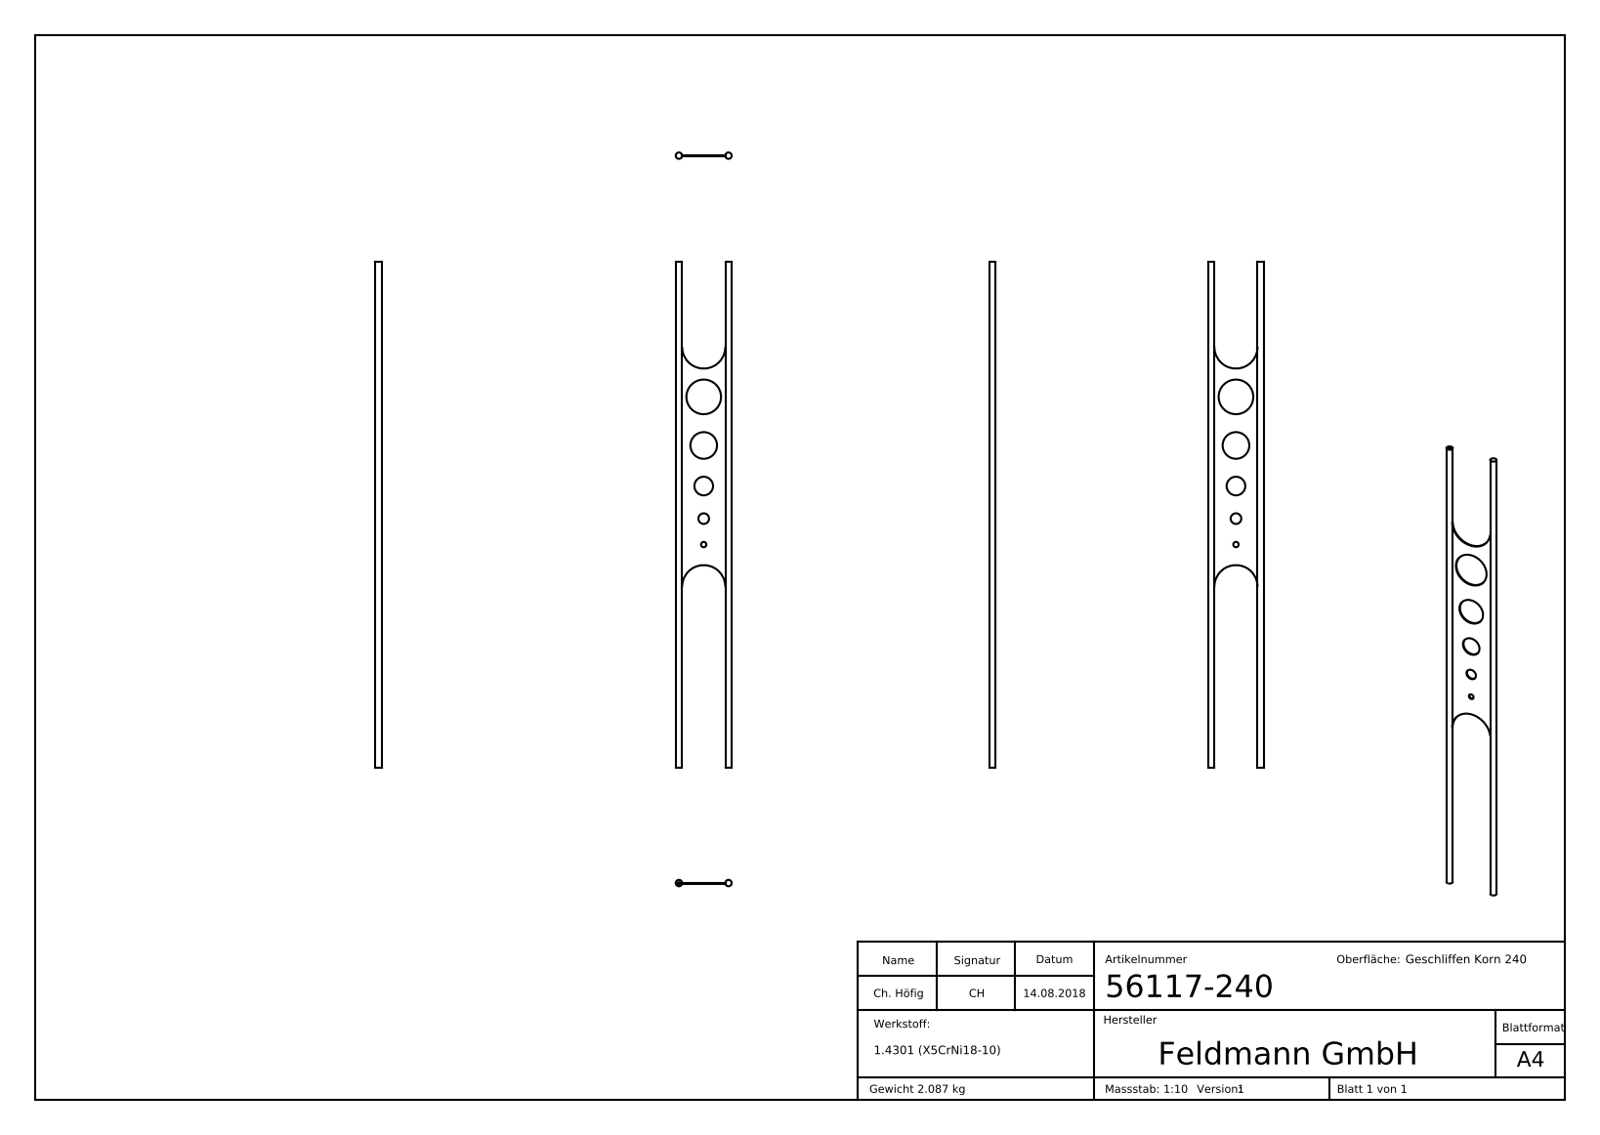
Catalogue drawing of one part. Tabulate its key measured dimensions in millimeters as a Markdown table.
| quantity | value |
| --- | --- |
| part name | 56117-240 |
| STEP written by | SolidWorks 2015 (CONFIG_CONTROL_DESIGN) |
| units | millimeters |
| bodies | 3 solids, 243 faces (143 planar, 20 cylindrical, 80 other) |
| overall size | 950 × 105 × 12 |
| volume | 165 570 mm³ |
| surface area | 124 862 mm² |
| round bosses / shafts (diameter × count) | 12 × 2, 65 × 1, 50 × 1, 35 × 1, 20 × 1, 10 × 1 |
| partial cylindrical surfaces (radius × count) | 40.5 × 2 |
| main face-to-face distances | 2, 81, 950, 949.5, 0.5, 0.53, 0.61, 2.61, 2.53, 2.33 |
